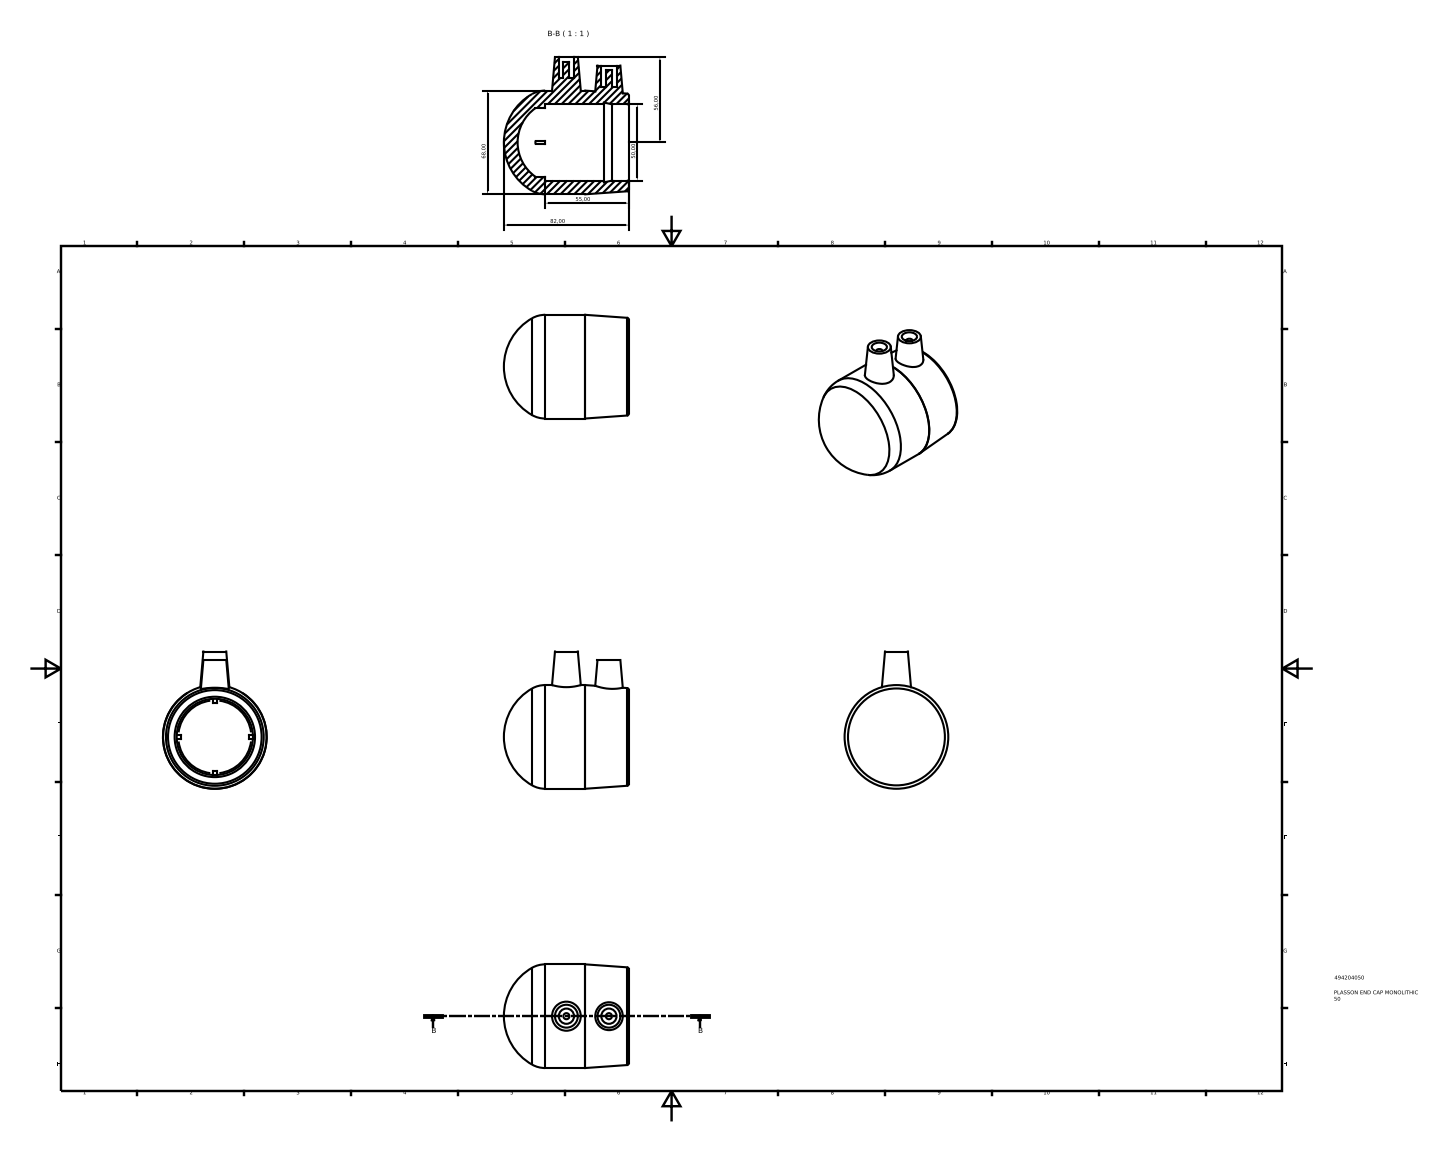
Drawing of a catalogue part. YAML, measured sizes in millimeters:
part_name: "494204050"
step_written_by: "Autodesk Inventor 2015 (AUTOMOTIVE_DESIGN)"
units: millimeters
bodies: {solids: 1, faces: 45, planar: 24, cylindrical: 7, other: 14}
overall_size: [90, 82, 68]
volume: 132570
surface_area: 33893
round_holes:
  - {diameter: 10, count: 2}
  - {diameter: 50, count: 1}
round_bosses_or_shafts:
  - {diameter: 4, count: 2}
  - {diameter: 68, count: 1}
face_to_face_distances: [16.4, 5.6, 14, 8.4, 19.6, 21.25, 23.75, 2.5, 45, 11]
hole_center_spacings: [27.88]
